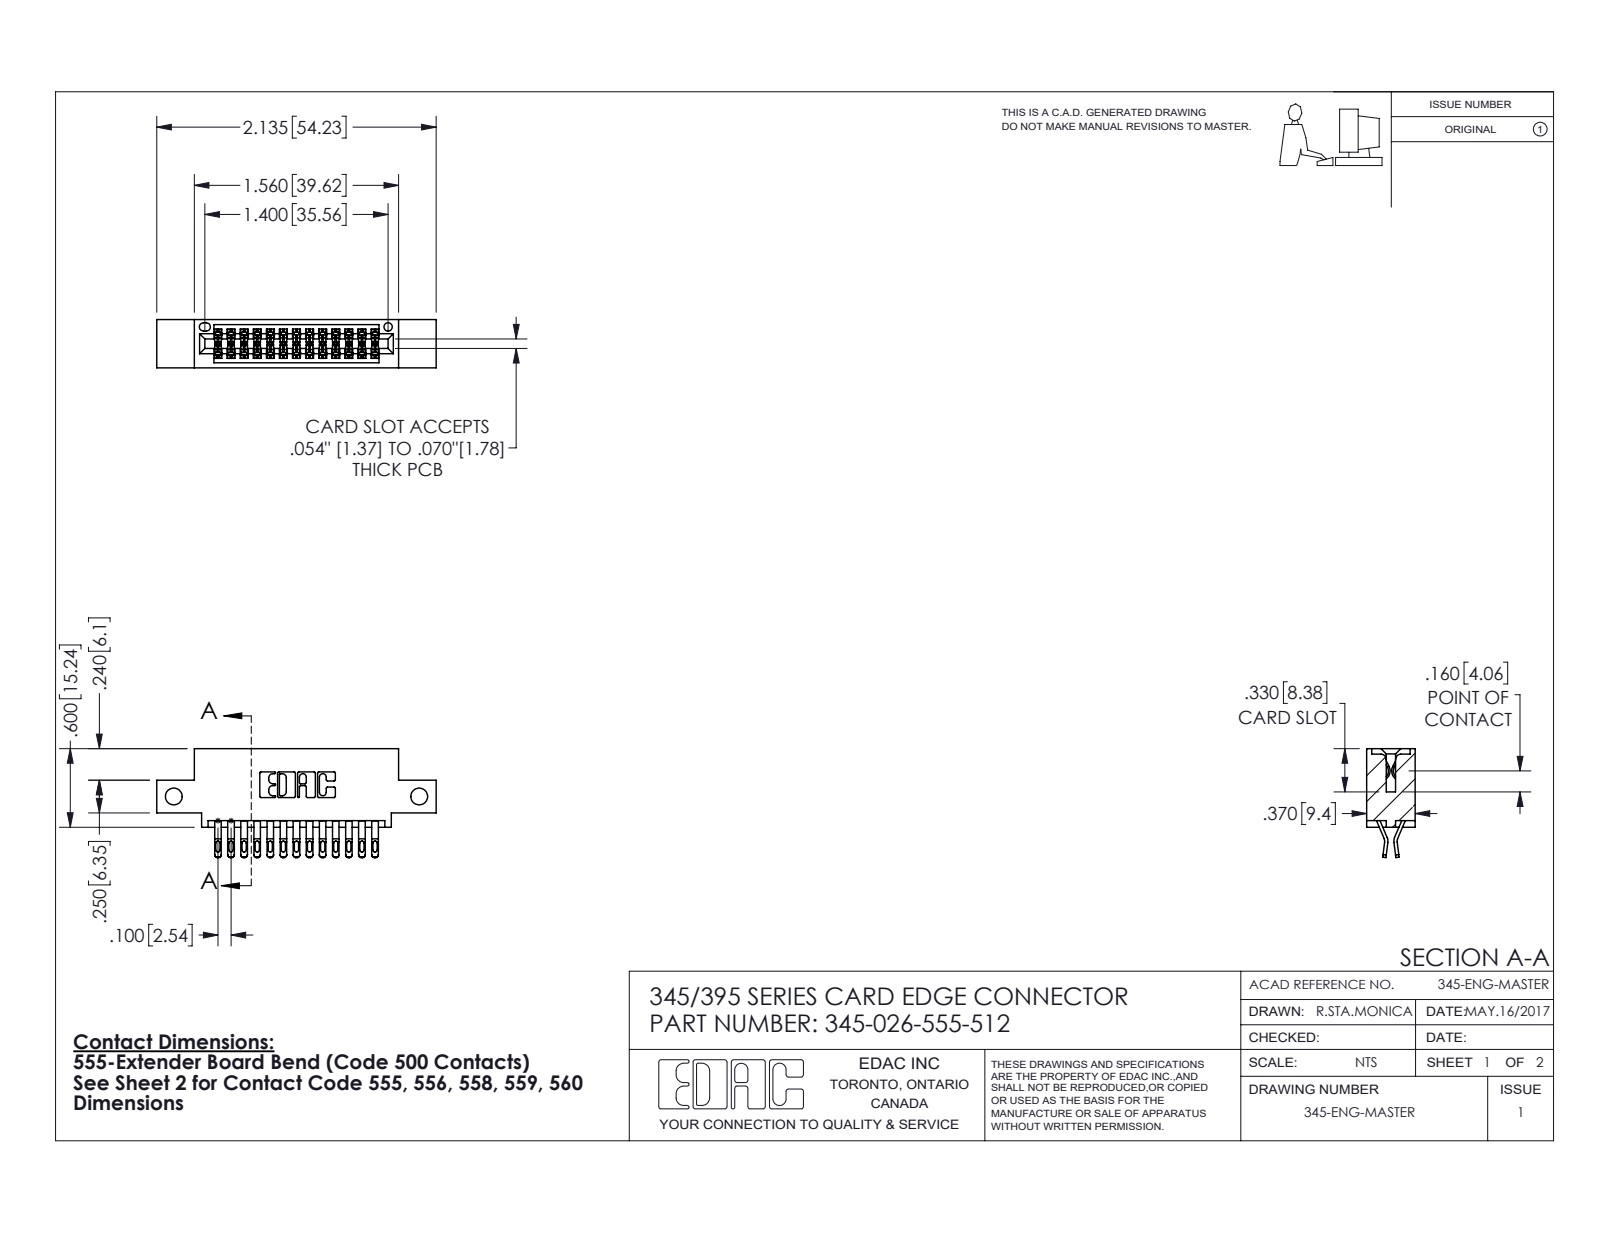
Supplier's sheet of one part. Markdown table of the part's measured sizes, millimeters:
| quantity | value |
| --- | --- |
| part name | 345-292-001_555 Tail; 345 Part_0.110 Offset - Side Mount; 345-026-555-512 |
| STEP written by | SolidWorks 2016 (CONFIG_CONTROL_DESIGN) |
| units | millimeters |
| bodies | 27 solids, 1586 faces (890 planar, 696 cylindrical, 0 other) |
| overall size | 54.2 × 21.1 × 9.4 |
| volume | 4 920 mm³ |
| surface area | 6 923 mm² |
| round holes (diameter × count) | 3.3 × 2, 1.6 × 1 |
| partial cylindrical surfaces (radius × count) | 0.4 × 65, 0.5 × 52, 0.2 × 39, 0.3 × 22, 0.2 × 6, 0.8 × 6, 0.7 × 3, 0.3 × 2 |
| main face-to-face distances | 7.6, 1.8, 5.1, 9.4, 0.6, 2.5, 6.9, 5.7, 2.5, 4.1 |
| hole center spacings | 47.6 |
